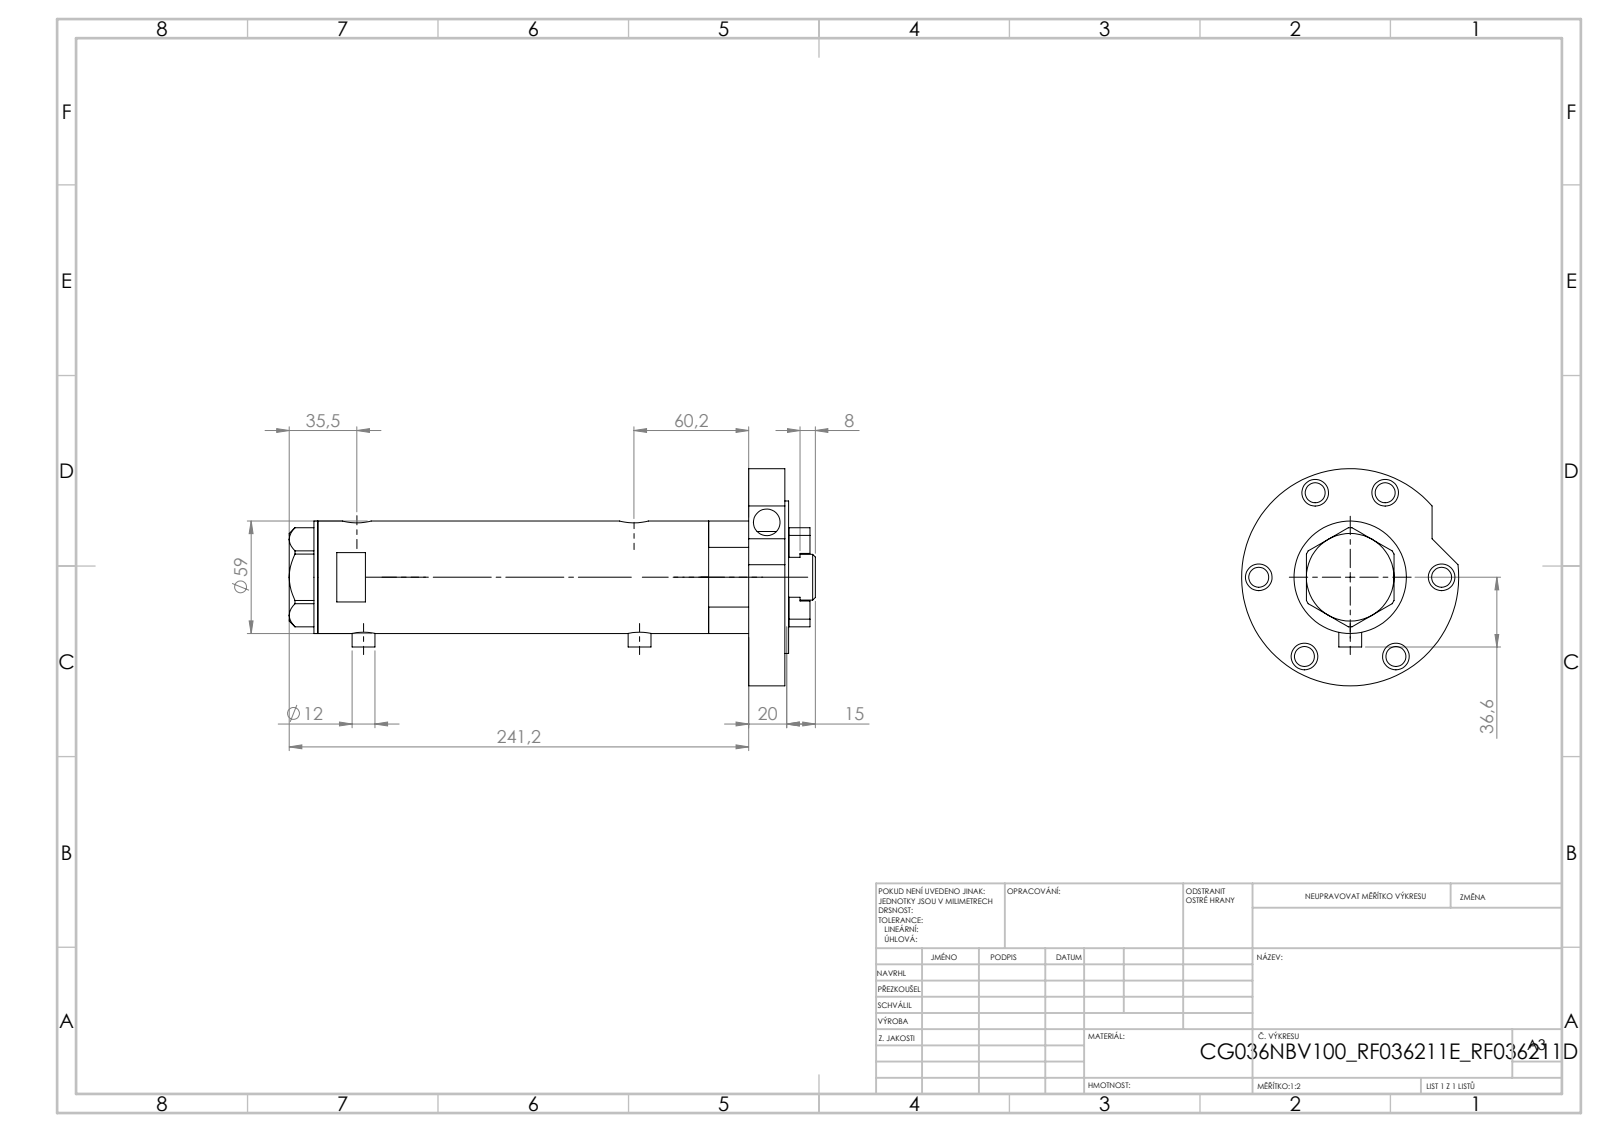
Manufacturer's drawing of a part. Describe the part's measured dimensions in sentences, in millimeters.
The part is named "V270CG_RF211E; V270CG_RF211D; V270CG_BACK; V270CG_VC (+2 more)". Its 3-D file was written by "SolidWorks 2019 (CONFIG_CONTROL_DESIGN)". It is 7 solids with 210 faces: 88 planar, 102 cylindrical and 20 other. Overall it measures 263.42 by 114 by 114 millimeters. Its volume is 733 285 cubic millimeters and its surface area 157 245 square millimeters. Round holes: 10 of diameter 10.5, 7 of diameter 14, 4 of diameter 6.1, 2 of diameter 5, 2 of diameter 9.73, 2 of diameter 12.5, 2 of diameter 15, 1 of diameter 8.5, 1 of diameter 25, 1 of diameter 26.5, 1 of diameter 36, 1 of diameter 40. Round bosses or shafts: 2 of diameter 12, 1 of diameter 114, 1 of diameter 80, 1 of diameter 59, 1 of diameter 46, 1 of diameter 24. The main face-to-face distances are 19.01, 21, 1.99, 210.84, 229.85, 231.84, 157.34, 53.5, 72.51, 74.5. The hole center spacings are 48, 19.92, 46.09, 57.24, 2.9, 3.5, 12, 28.22.
